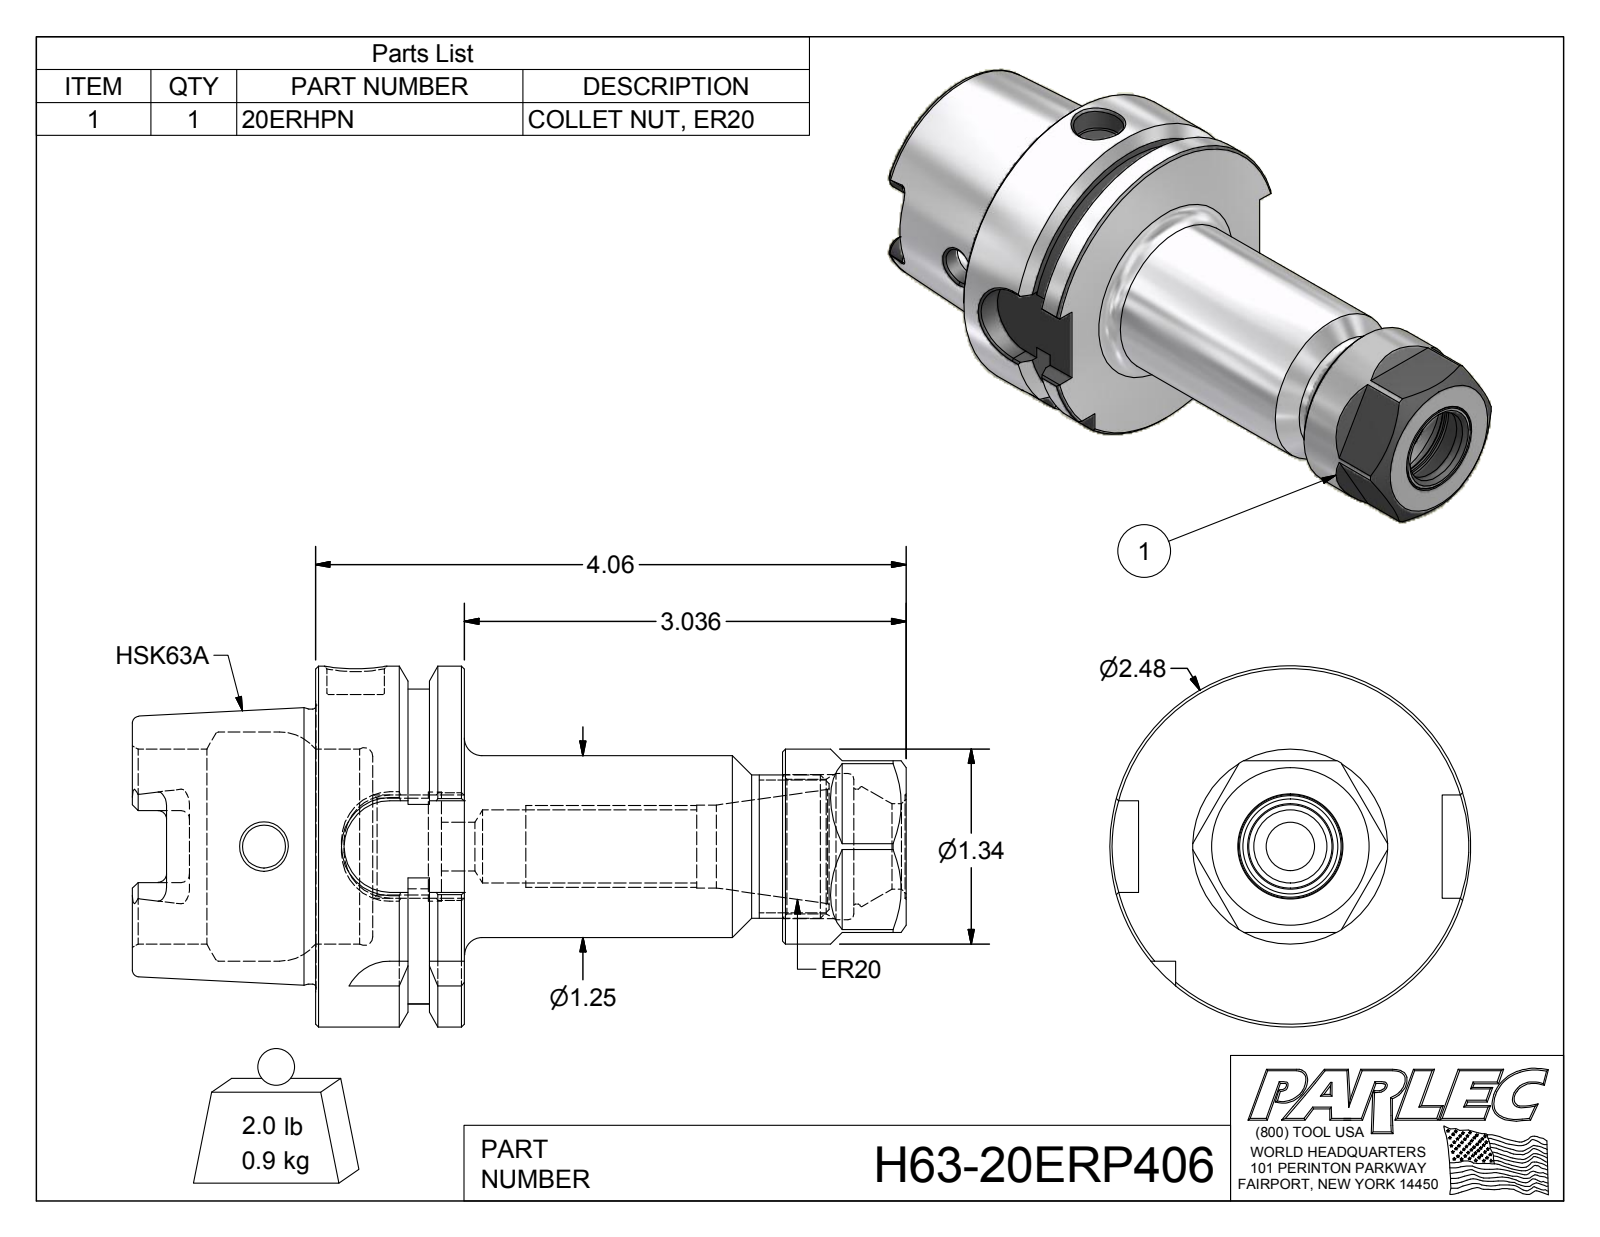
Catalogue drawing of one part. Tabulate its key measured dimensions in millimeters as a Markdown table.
| quantity | value |
| --- | --- |
| part name | H63-20ERP406; H63-20ER4-1; 20ERHPN |
| STEP written by | Autodesk Inventor 2012 (AUTOMOTIVE_DESIGN) |
| units | millimeters |
| bodies | 2 solids, 171 faces (68 planar, 41 cylindrical, 62 other) |
| overall size | 135.1 × 63 × 63 |
| volume | 126 700 mm³ |
| surface area | 35 690 mm² |
| round holes (diameter × count) | 7.5 × 1, 8.5 × 1, 10 × 1, 12.8 × 1, 14.5 × 1, 14.9 × 1, 16.9 × 1, 19 × 1, 20.1 × 1, 23.5 × 1, 25.5 × 1, 34 × 1 |
| round bosses / shafts (diameter × count) | 63 × 1, 48 × 1, 34 × 1, 31.8 × 1, 25 × 1 |
| partial cylindrical surfaces (radius × count) | 1.5 × 6, 2.9 × 4, 8 × 4, 27.5 × 1 |
| main face-to-face distances | 26, 6.1, 9.9, 10, 16, 30, 32, 42, 58, 113.5 |
